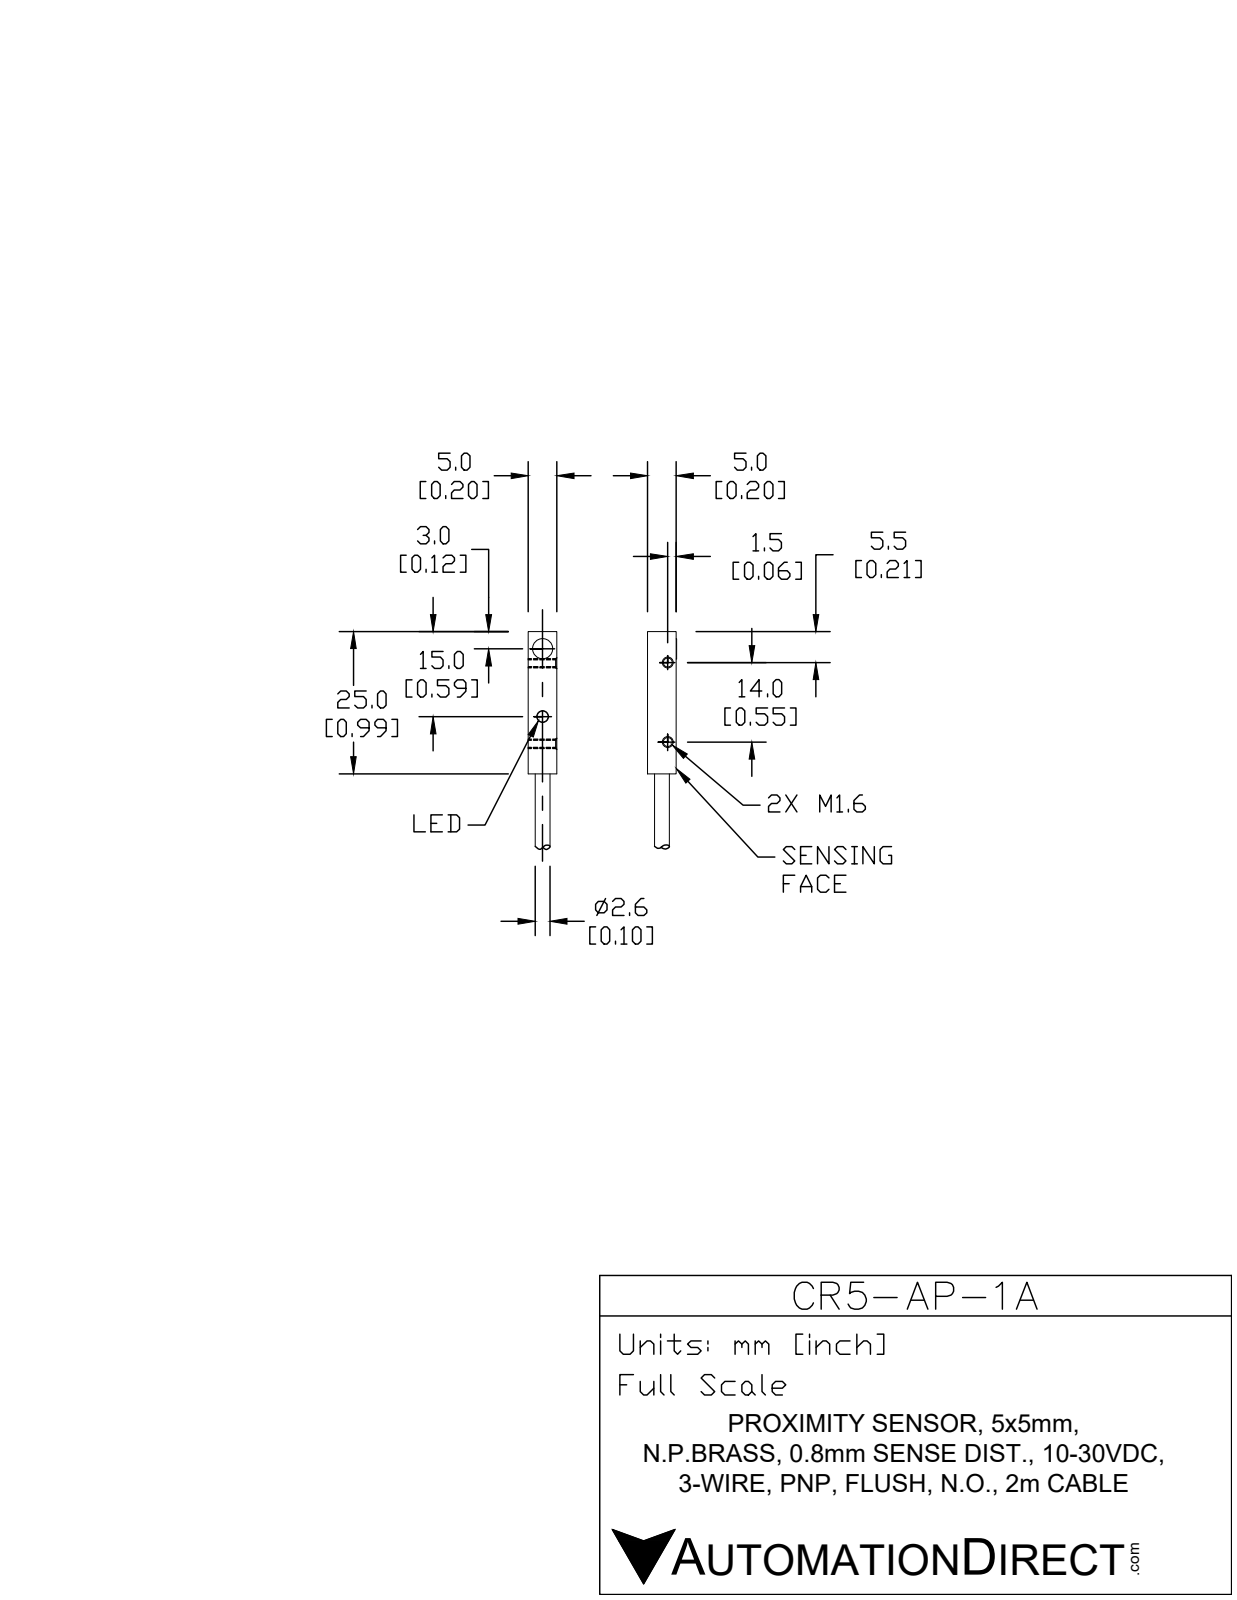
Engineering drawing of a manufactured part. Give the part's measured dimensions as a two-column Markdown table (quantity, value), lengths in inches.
| quantity | value |
| --- | --- |
| part name | CR5-AP-1A |
| STEP written by | SolidWorks 2017 (AUTOMOTIVE_DESIGN) |
| units | inches |
| bodies | 1 solid, 18 faces (8 planar, 5 cylindrical, 5 other) |
| overall size | 1.772 × 0.197 × 0.197 |
| volume | 0.044 in³ |
| surface area | 1.162 in² |
| round holes (diameter × count) | 0.048 × 2, 0.039 × 1, 0.102 × 1 |
| round bosses / shafts (diameter × count) | 0.102 × 1 |
| main face-to-face distances | 0.197, 0.984, 0.187, 0.787, 1.772 |
| hole center spacings | 0.472, 0.551 |
